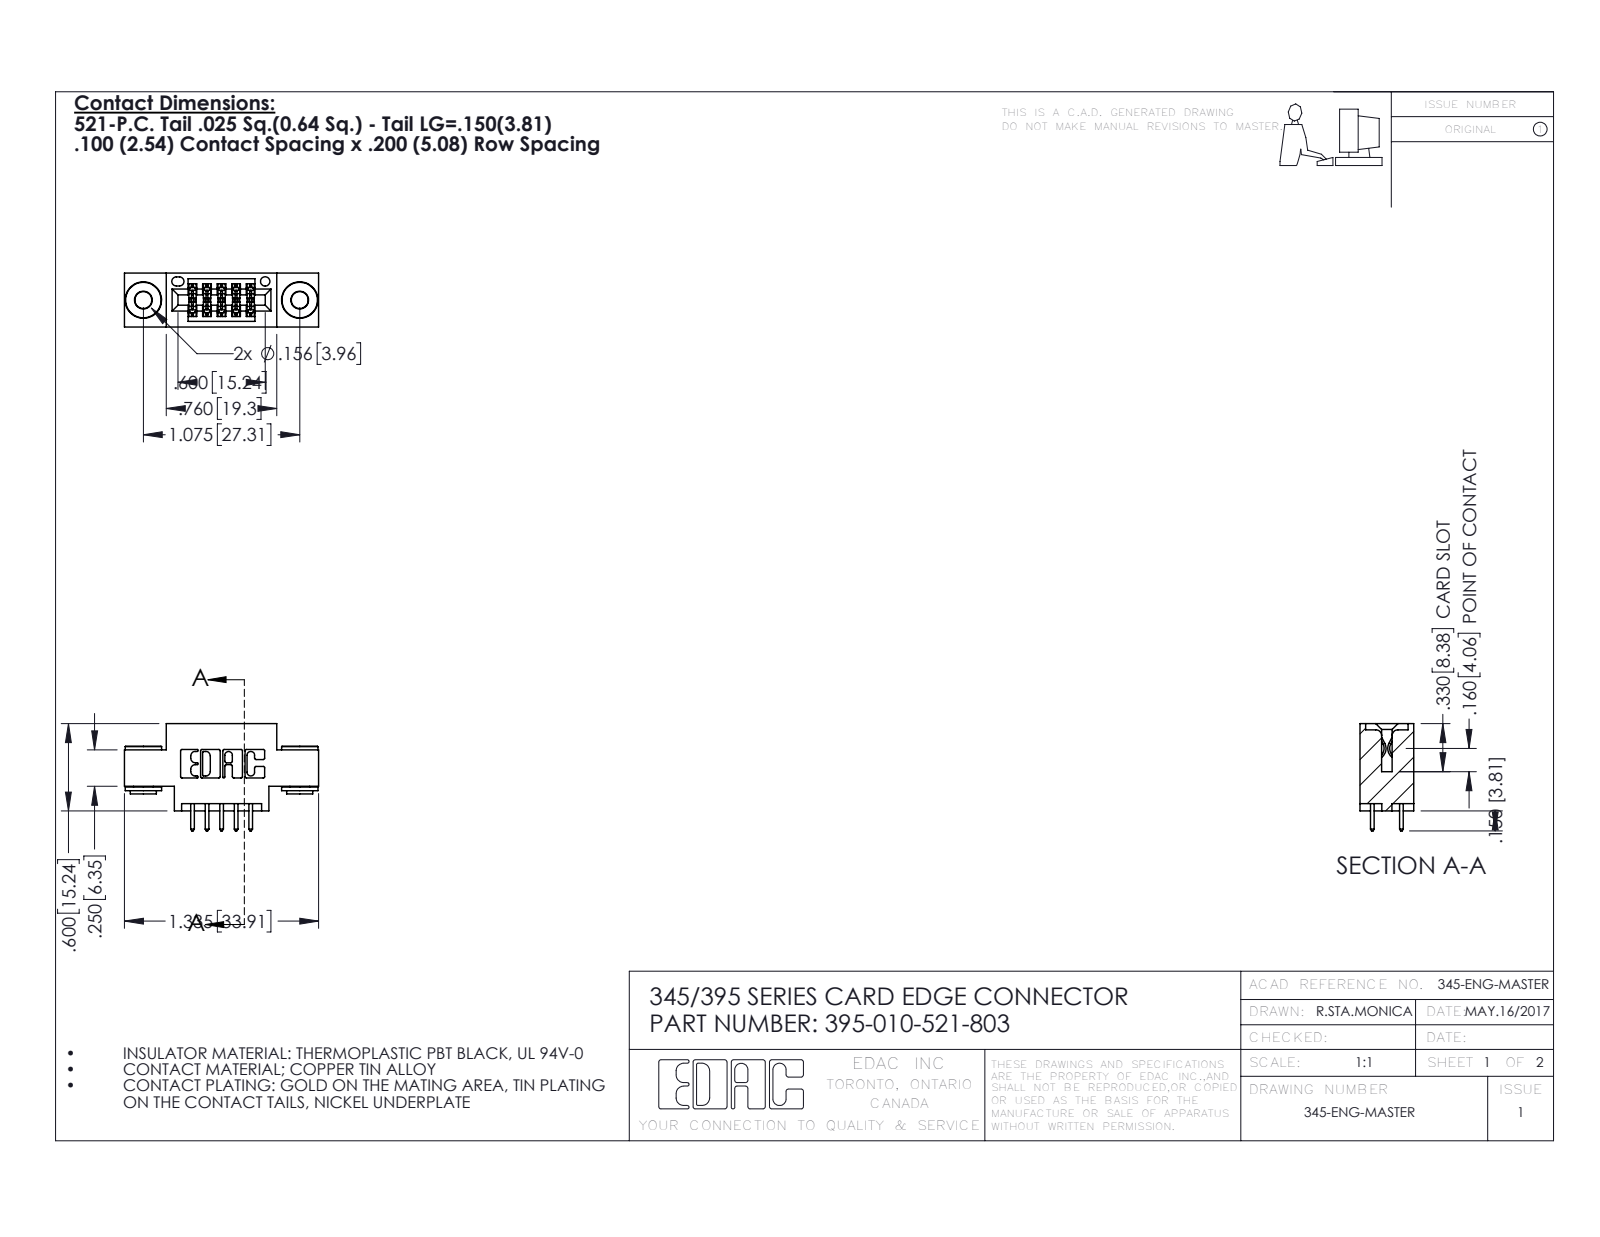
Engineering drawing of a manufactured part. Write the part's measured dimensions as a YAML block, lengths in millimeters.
part_name: "345 Part_0.170 Offset - 0.156 Dia-TH; 345-250-002_345-250-002-102; 395-010-521-803; 345-292-001_345-293-121"
step_written_by: "SolidWorks 2016 (CONFIG_CONTROL_DESIGN)"
units: millimeters
bodies: {solids: 13, faces: 668, planar: 424, cylindrical: 236, other: 8}
overall_size: [33.9, 18.7, 9.4]
volume: 2850
surface_area: 3821
round_holes:
  - {diameter: 2.9, count: 2}
  - {diameter: 4, count: 2}
  - {diameter: 1.6, count: 1}
round_bosses_or_shafts:
  - {diameter: 6.4, count: 2}
  - {diameter: 4.6, count: 2}
  - {diameter: 3.5, count: 2}
partial_cylinders:
  - {radius: 0.3, count: 22}
  - {radius: 0.2, count: 15}
  - {radius: 0.3, count: 10}
  - {radius: 0.2, count: 6}
  - {radius: 0.8, count: 6}
  - {radius: 0.7, count: 3}
  - {radius: 0.4, count: 2}
  - {radius: 0.5, count: 2}
face_to_face_distances: [9.4, 5.1, 1.8, 7.6, 2.5, 6.4, 0.6, 2.5, 6.9, 5.7]
hole_center_spacings: [6.9, 21.5, 27.3]
